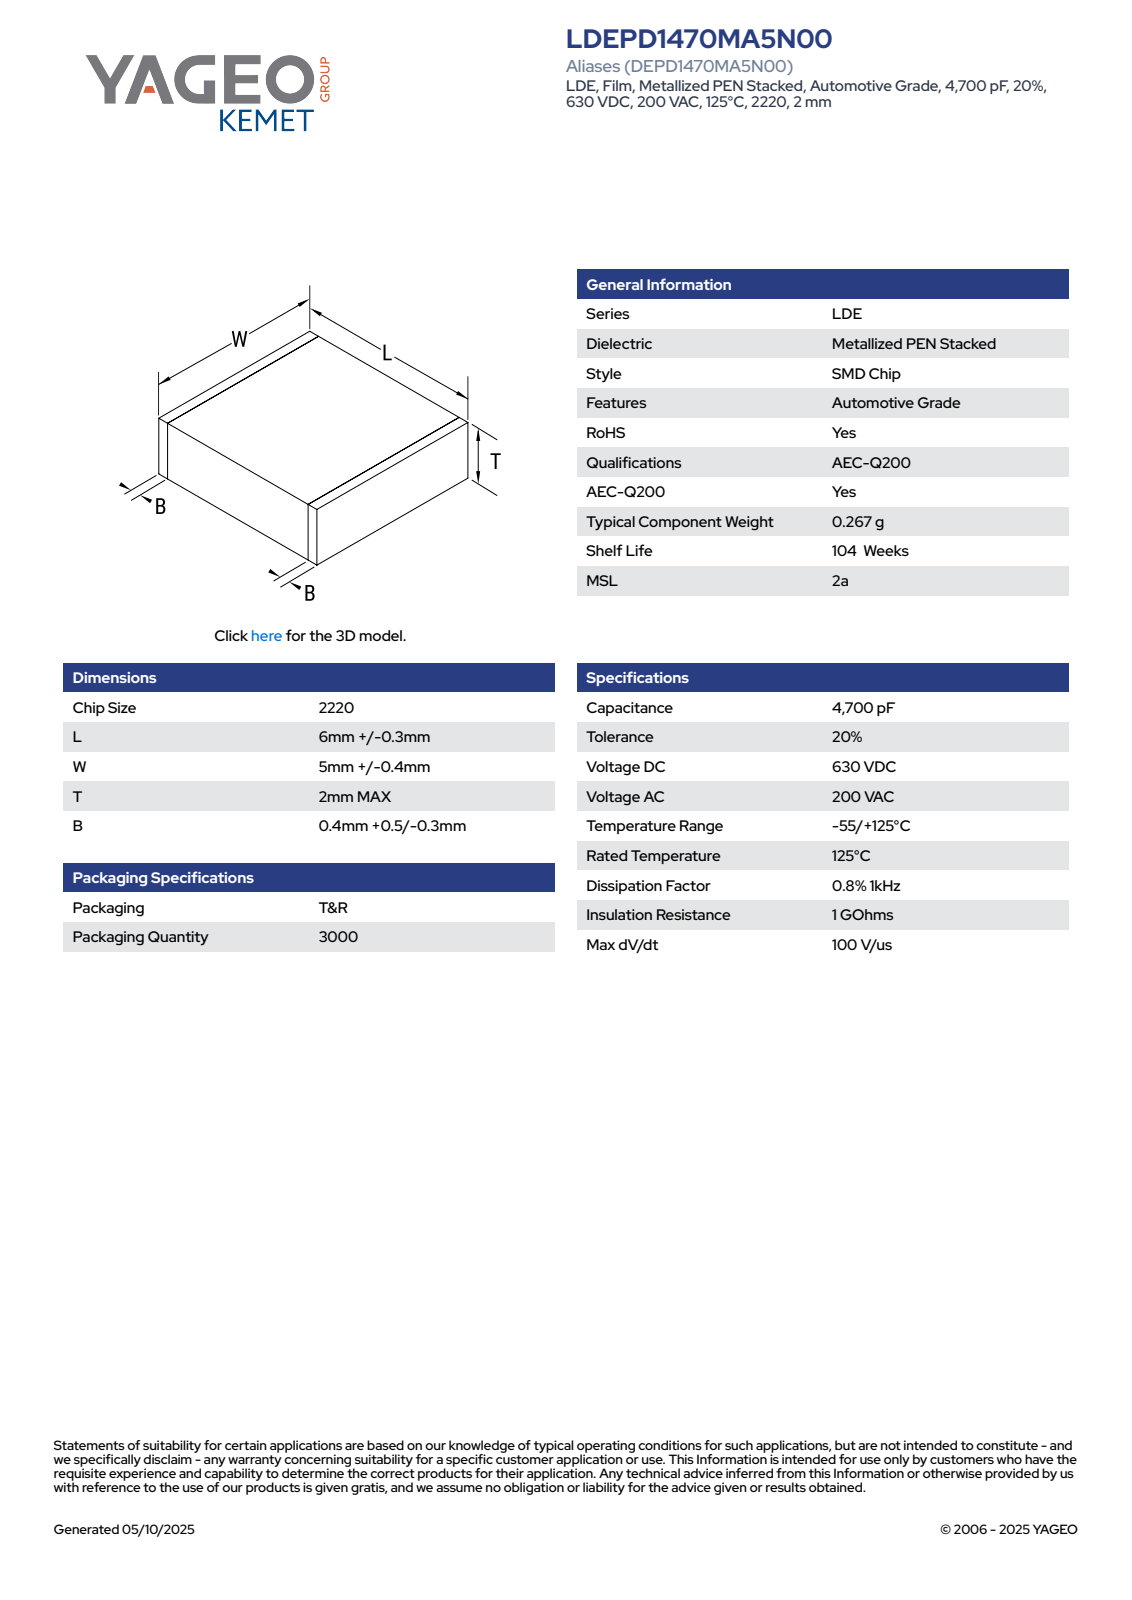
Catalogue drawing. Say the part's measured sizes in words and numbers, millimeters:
The part is named "CFS_LDELDB_2220_L6.3W5.4T2B0.9". Its 3-D file was written by "SolidWorks 2020 (AUTOMOTIVE_DESIGN)". It is 4 solids with 73 faces: 73 planar, 0 cylindrical and 0 other. Overall it measures 6.3 by 5.4 by 2 millimeters. Its volume is 67 cubic millimeters and its surface area 117 square millimeters. The main face-to-face distances are 1.98, 6.3, 1.99, 5.38, 2, 5.39, 5.4, 0.5, 5.8, 5.3.
